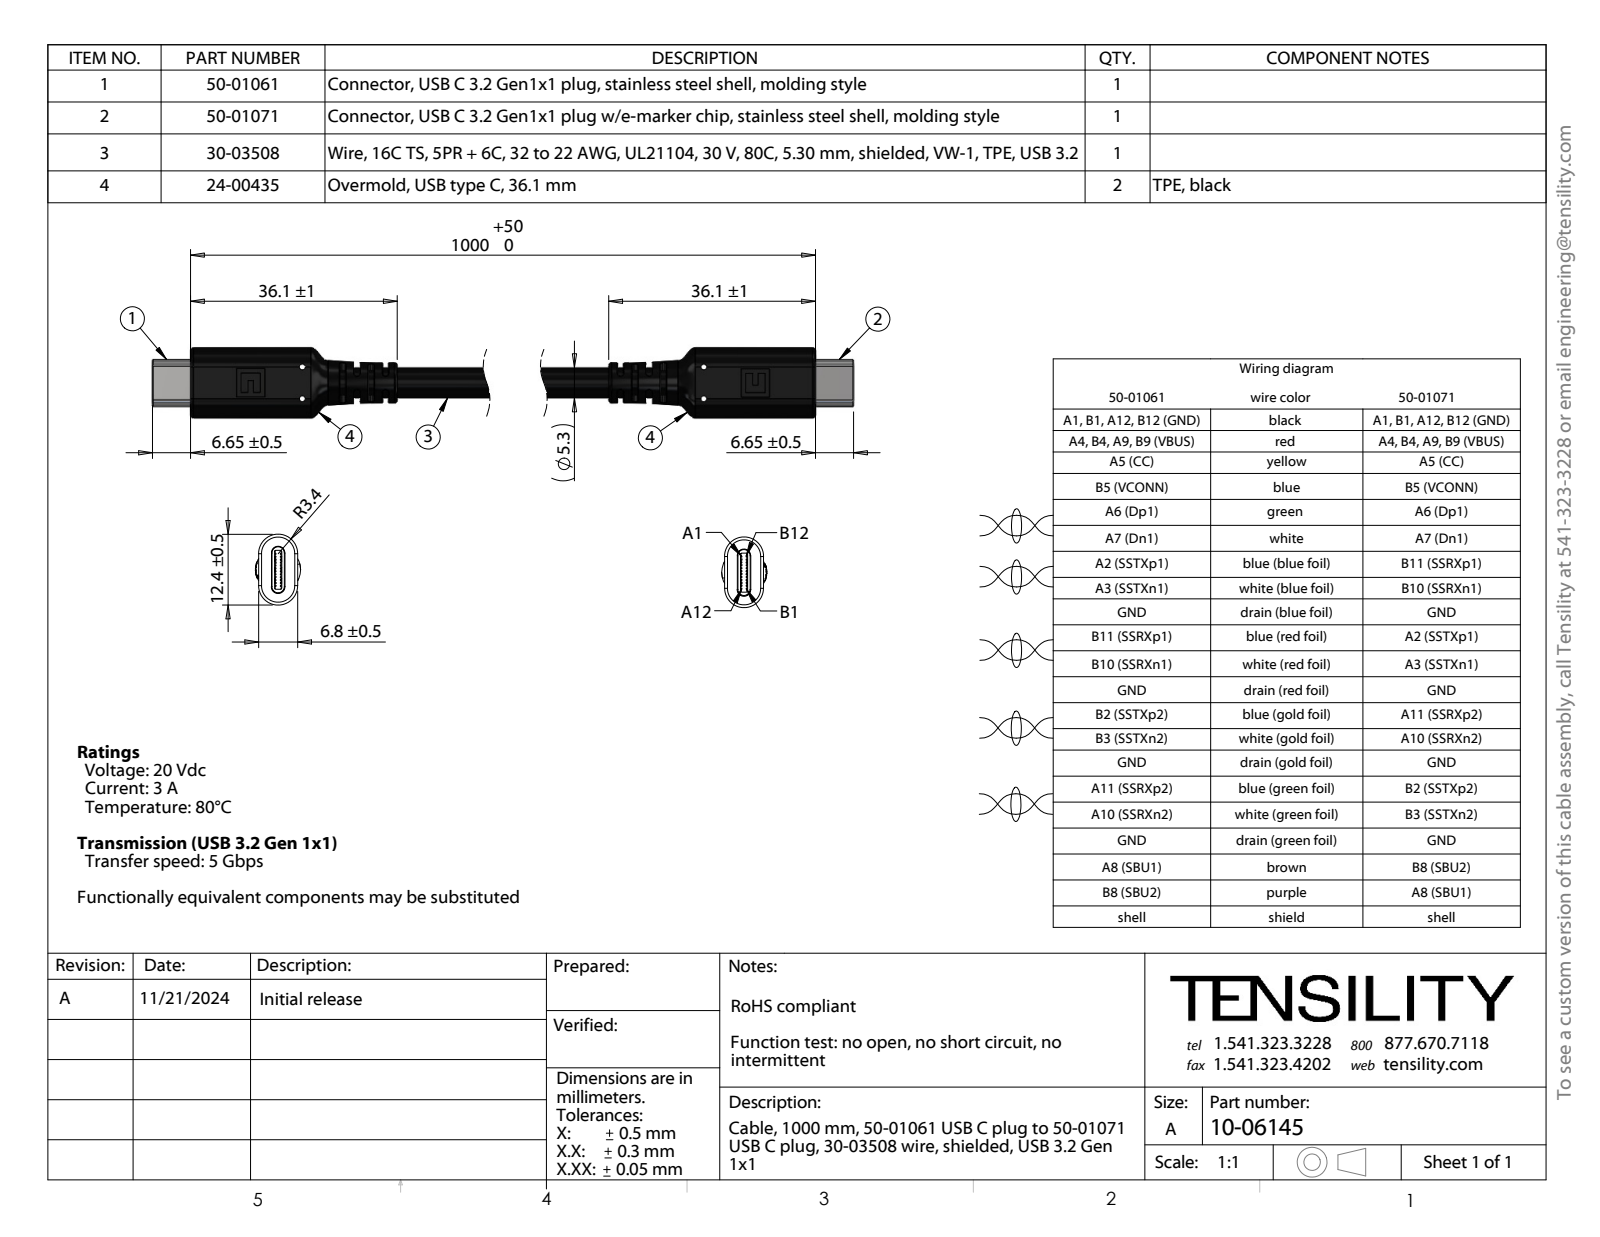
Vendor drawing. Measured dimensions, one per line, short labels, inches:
name: 30-03508; 10-06145; 50-01061_Hidden emarker; 24-00435 (+1 more)
written by: SolidWorks 2021 (CONFIG_CONTROL_DESIGN)
unit: in
bodies: 168 solids, 1726 faces (728 planar, 766 cylindrical, 232 other)
size: 8.48 × 0.486 × 0.311
volume: 0.413 in³; area: 76.59 in²
holes: 4× ⌀0.039, 1× ⌀0.164, 1× ⌀0.164, 1× ⌀0.165, 1× ⌀0.165, 1× ⌀0.173
bosses: 8× ⌀0.029, 4× ⌀0.019, 4× ⌀0.01, 2× ⌀0.022, 1× ⌀0.308, 1× ⌀0.209, 1× ⌀0.039, 1× ⌀0.035
rounds: 20× R0.02, 8× R0.01, 4× R0.004, 4× R0.006, 4× R0.046, 2× R0.012, 2× R0.012, 2× R0.019
face distances: 0.041, 0.041, 0.037, 0.04, 0.043, 0.268, 0.024, 0.098, 0.056, 0.212
hole spacings: 0.083, 0.097, 0.098, 0.08, 0.021, 0.025, 0.065, 0.081
